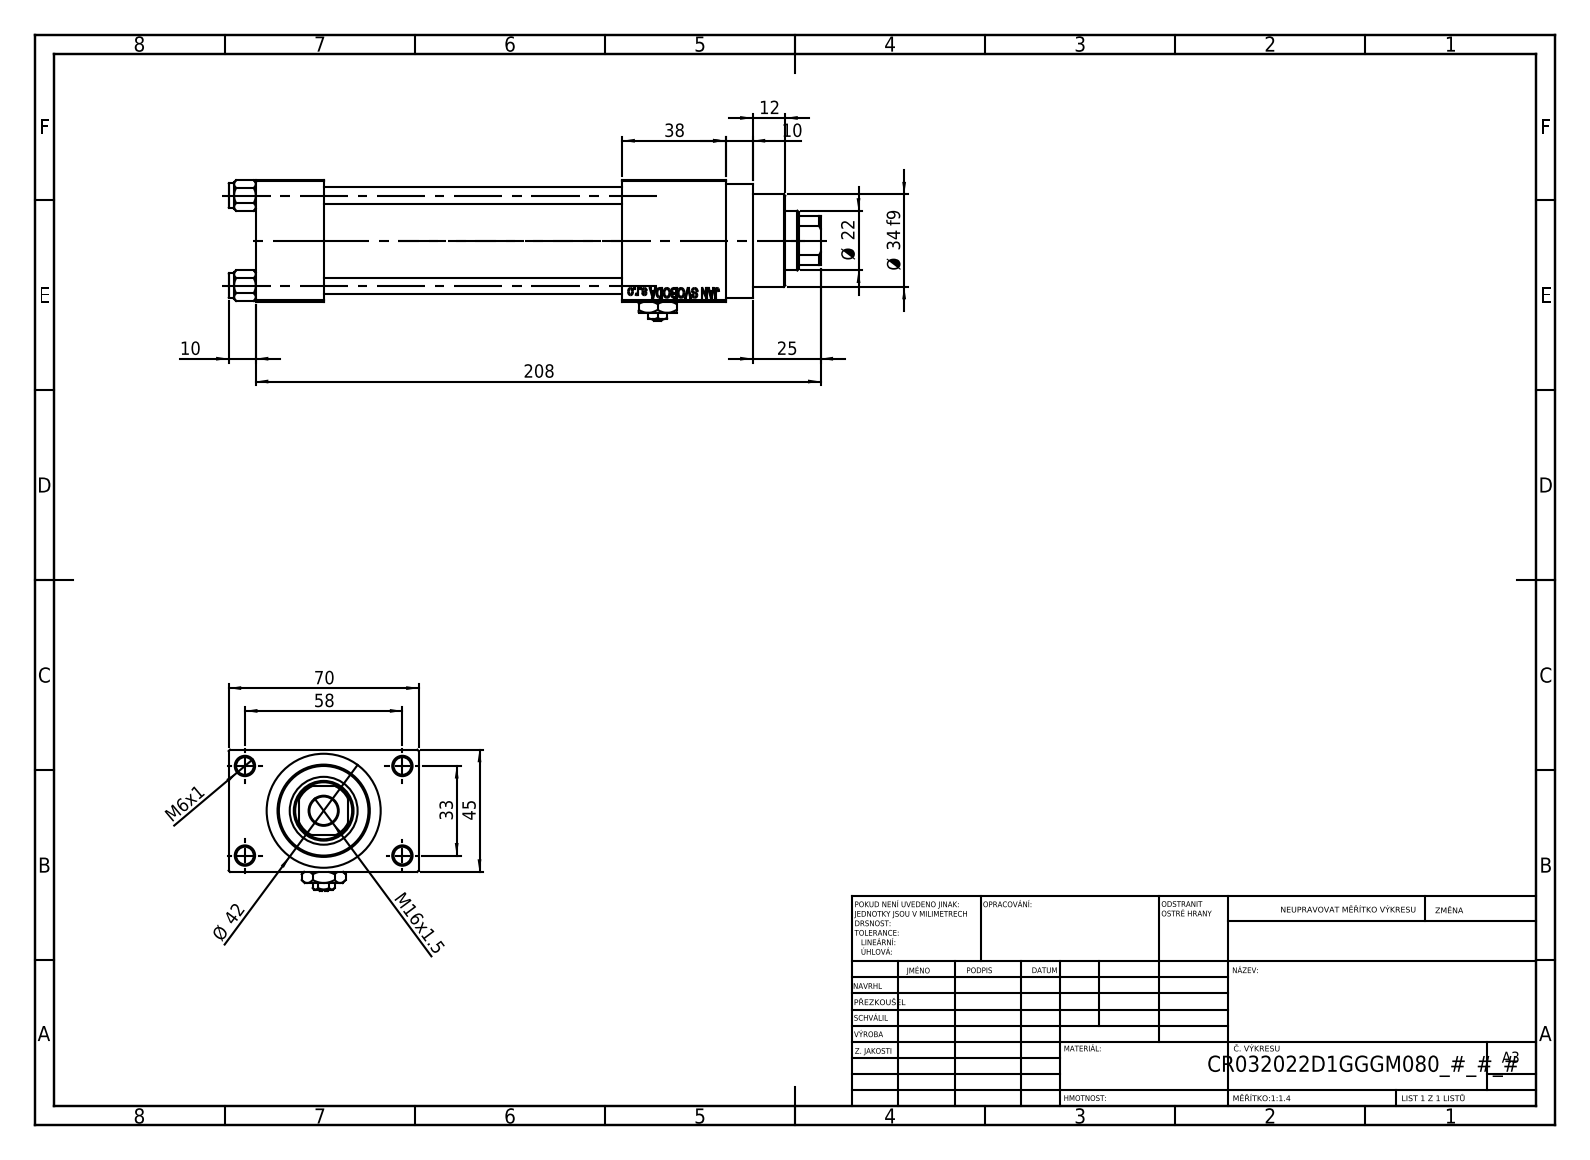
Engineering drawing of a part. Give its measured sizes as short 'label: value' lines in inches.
name: V215_VC_A; V215CR_D_Body; Zatka_pro_OIL_PORT; V215CR_VCP_D (+2 more)
written by: SolidWorks 2019 (CONFIG_CONTROL_DESIGN)
unit: in
bodies: 12 solids, 1150 faces (519 planar, 93 cylindrical, 538 other)
size: 8.583 × 2.756 × 2.047
volume: 17.94 in³; area: 158 in²
holes: 4× ⌀0.236, 4× ⌀0.256, 2× ⌀0.276, 2× ⌀0.518, 2× ⌀0.787, 1× ⌀0.413, 1× ⌀0.866, 1× ⌀0.945, 1× ⌀0.984, 1× ⌀1.26, 1× ⌀1.299
bosses: 4× ⌀0.354, 1× ⌀1.654, 1× ⌀1.496, 1× ⌀1.339
rounds: 1× R0.413
face distances: 1.772, 0.984, 0.492, 2.264, 4.331, 5.315, 5.827, 2.756, 1.496, 6.811
hole spacings: 0.488, 0.924, 1.307, 1.314, 1.392, 1.795, 2.219, 1.299
